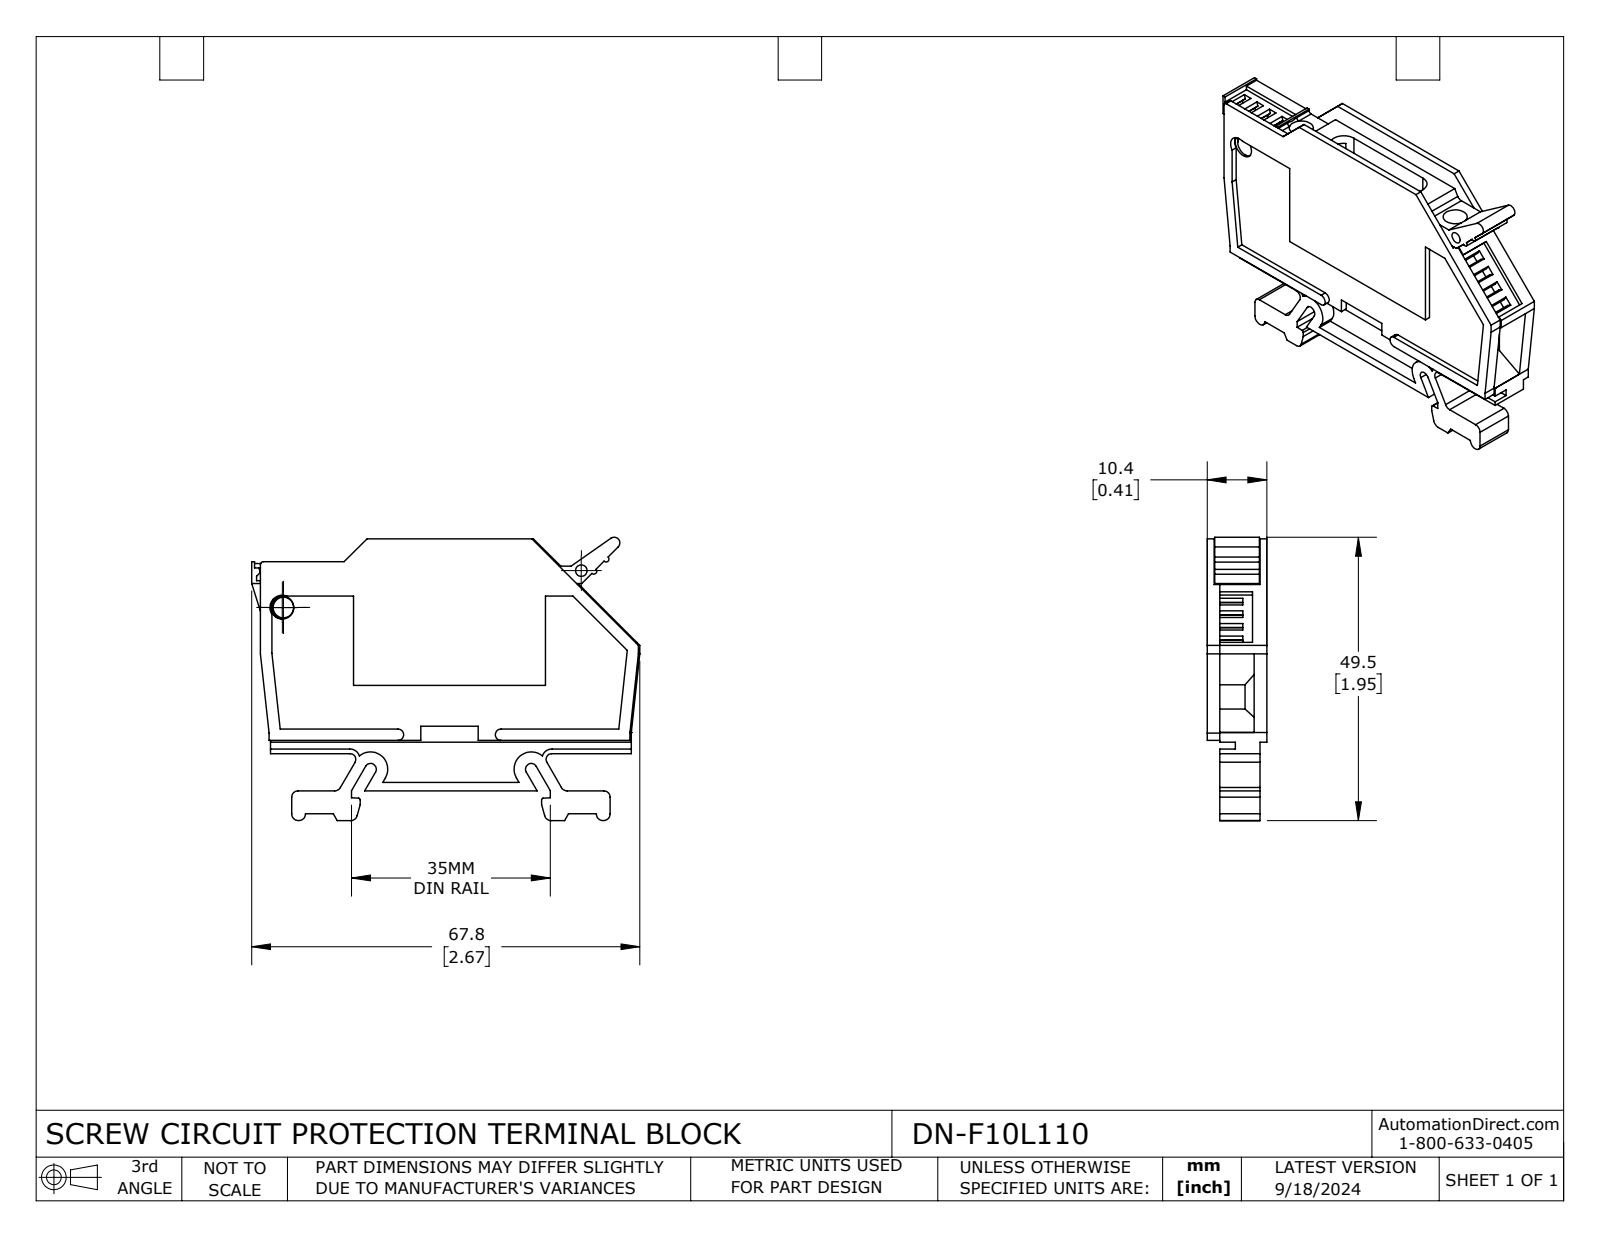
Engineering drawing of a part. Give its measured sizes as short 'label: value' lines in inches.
name: DN-F10L110
written by: SolidWorks 2023 (CONFIG_CONTROL_DESIGN)
unit: in
bodies: 1 solid, 440 faces (292 planar, 78 cylindrical, 70 other)
size: 2.669 × 1.948 × 0.409
volume: 0.902 in³; area: 21.57 in²
holes: 3× ⌀0.165, 2× ⌀0.079, 1× ⌀0.098, 1× ⌀0.157
bosses: 1× ⌀0.157
rounds: 12× R0.039, 6× R0.047, 4× R0.02, 3× R0.049, 3× R0.079, 2× R0.012, 2× R0.043, 2× R0.071
face distances: 0.047, 0.039, 0.358, 0.323, 0.362, 0.087, 0.311, 0.079, 0.051, 0.319
hole spacings: 0.826, 0.828, 1.496, 2.064, 2.072, 2.151
